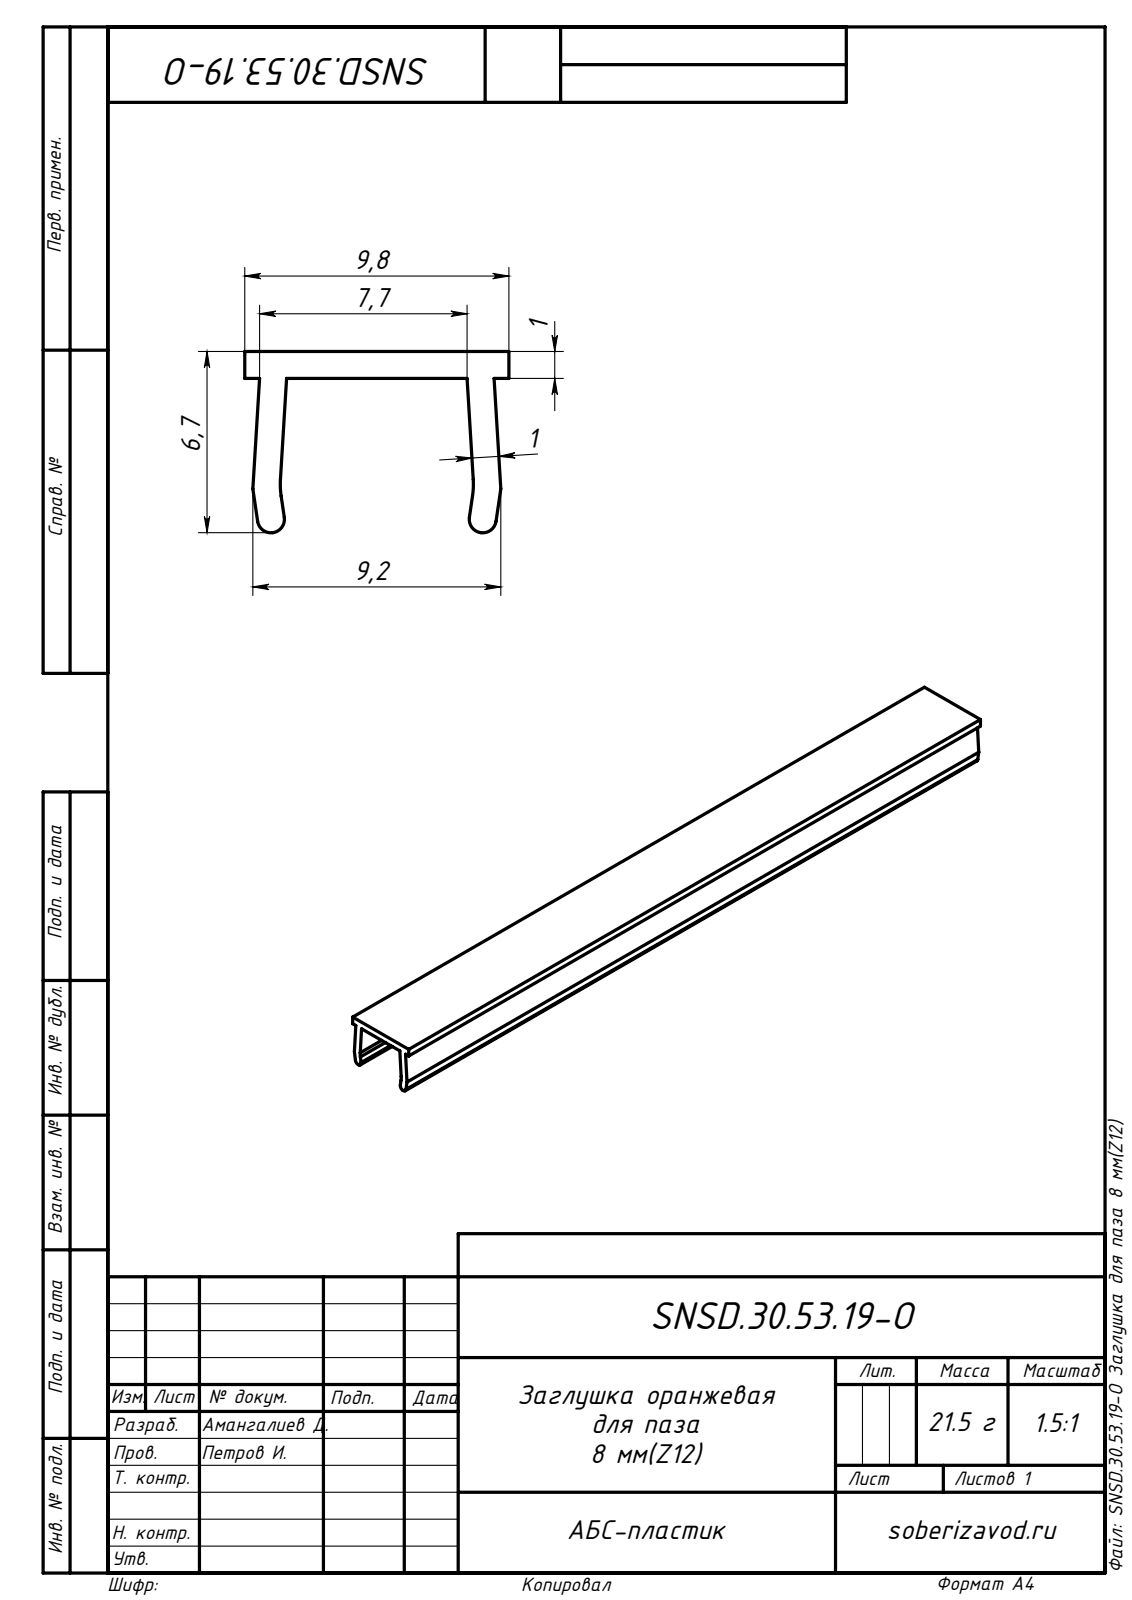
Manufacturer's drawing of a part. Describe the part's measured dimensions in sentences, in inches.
Its 3-D file was written by "SolidWorks 2017 (AUTOMOTIVE_DESIGN)". It is 1 solid with 24 faces: 16 planar, 8 cylindrical and 0 other. Overall it measures 39.37 by 0.386 by 0.265 inches. Its volume is 1.287 cubic inches and its surface area 67.87 square inches. Partial cylindrical surfaces (rounded edges, fillets, slot ends): 2 of radius 0.02, 2 of radius 0.118. The main face-to-face distances are 0.039, 0.386, 39.37.
